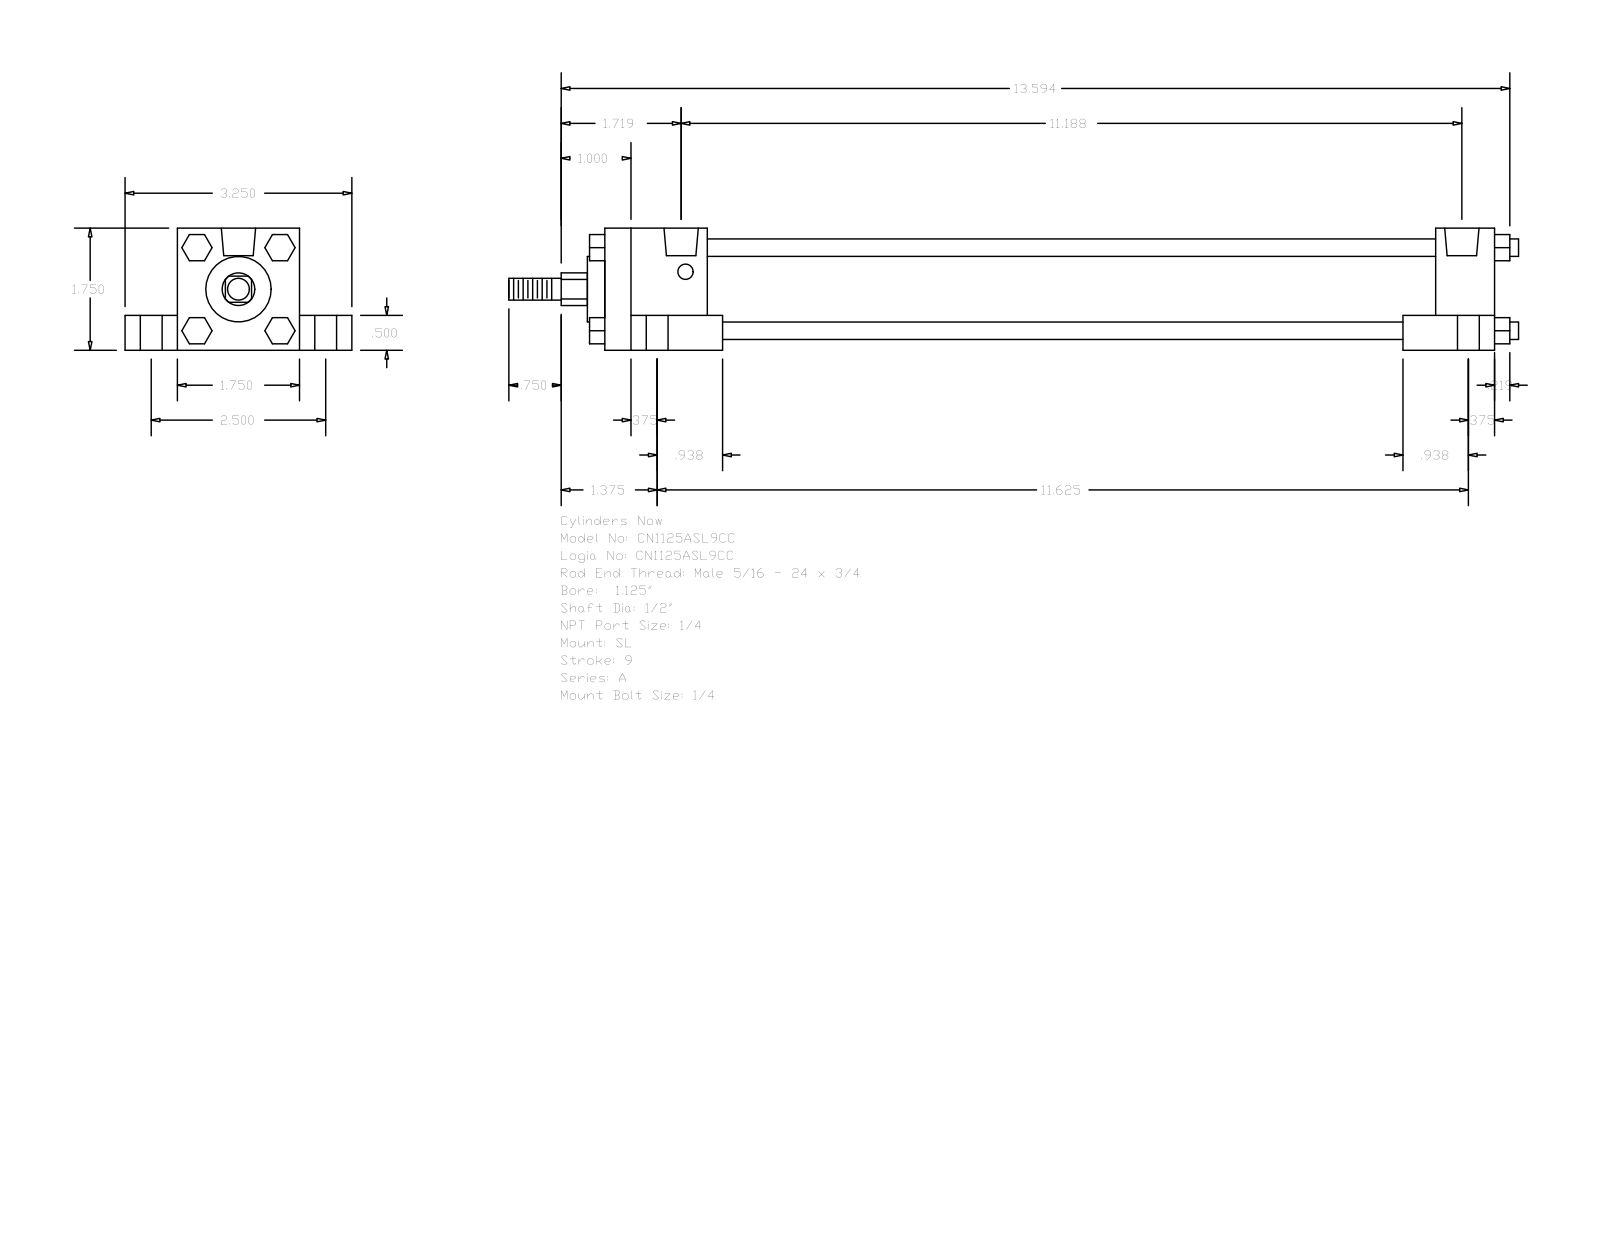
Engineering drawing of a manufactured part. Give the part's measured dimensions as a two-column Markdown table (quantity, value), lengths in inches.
| quantity | value |
| --- | --- |
| part name | A_SL__0112_0.5 |
| STEP written by | GSSL Pune (CONFIG_CONTROL_DESIGN) |
| units | inches |
| bodies | 0 solids, 150 faces (114 planar, 36 cylindrical, 0 other) |
| overall size | 14.469 × 3.25 × 1.75 |
| round holes (diameter × count) | 0.219 × 4, 0.313 × 4, 0.563 × 4, 0.492 × 2 |
| round bosses / shafts (diameter × count) | 0.25 × 4, 1.255 × 1, 0.937 × 1, 0.5 × 1, 0.313 × 1 |
| partial cylindrical surfaces (radius × count) | 0.234 × 1 |
| main face-to-face distances | 1.75, 1.25, 0.5, 0.75, 2.5, 12.75, 11.906, 0.844, 1.469, 10.437 |
| hole center spacings | 1.254, 1.26, 1.296, 1.315, 2.5, 11.063, 11.288, 11.35 |
